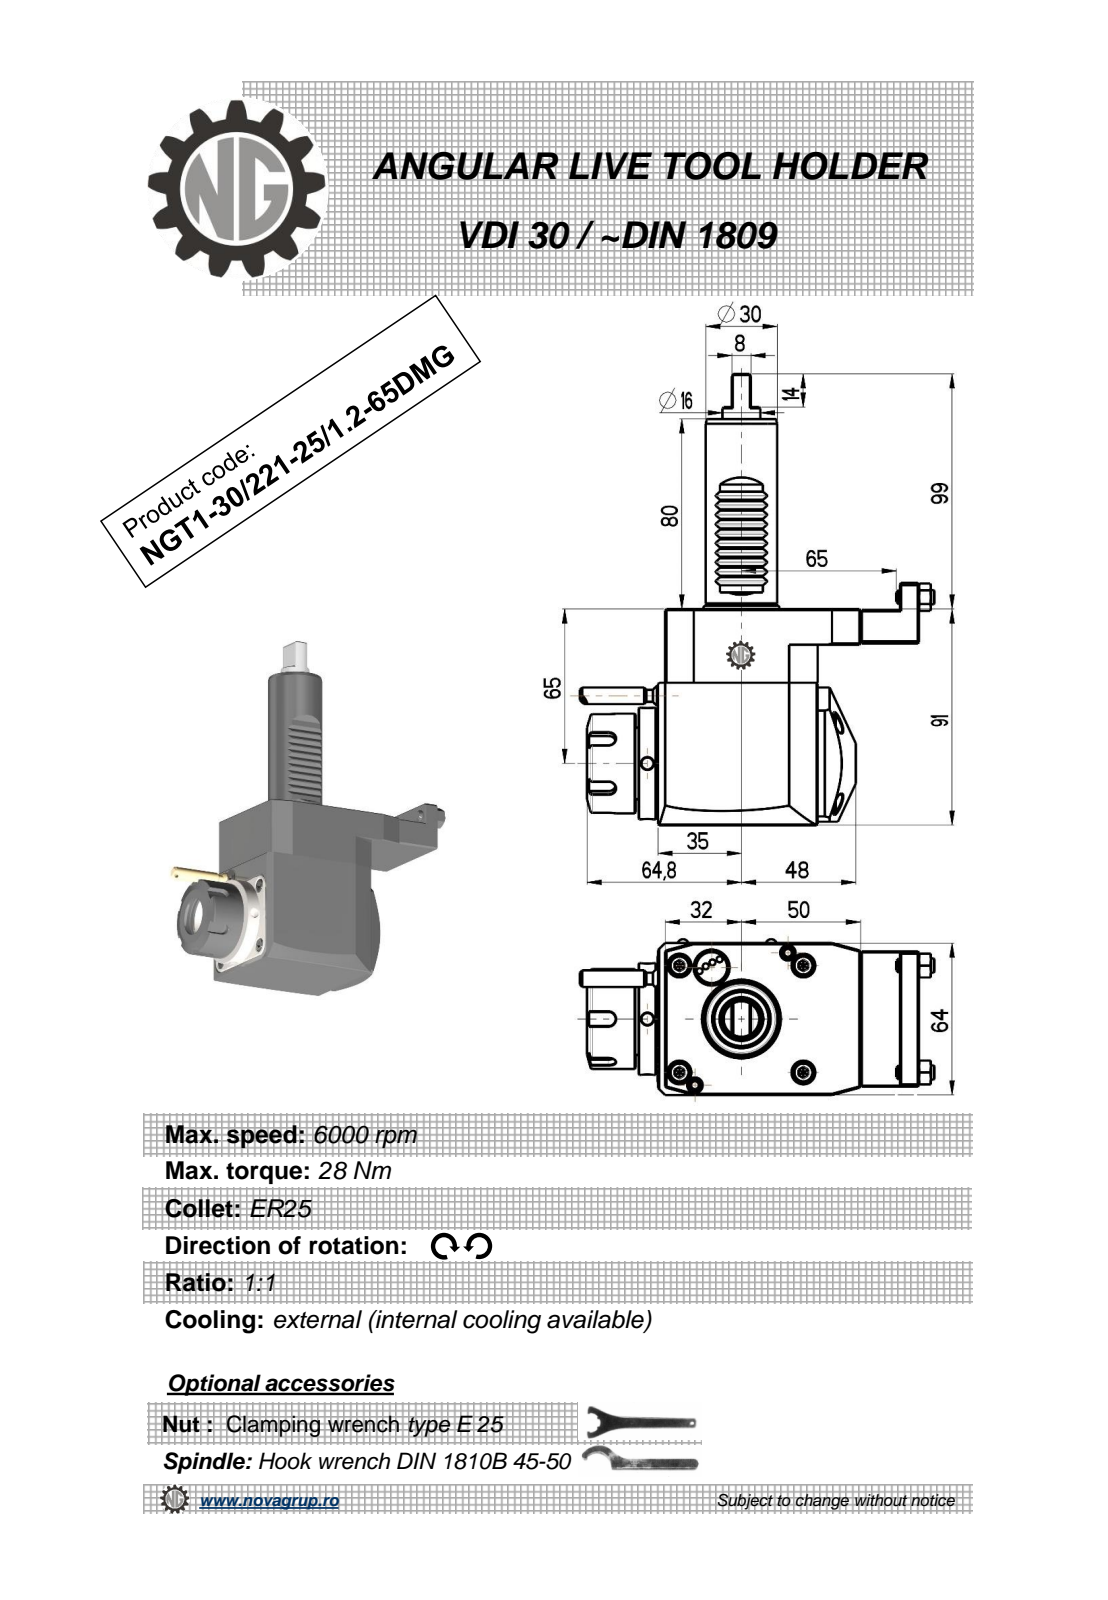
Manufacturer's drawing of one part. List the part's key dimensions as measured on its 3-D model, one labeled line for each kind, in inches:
Part name (STEP PRODUCT): NGT1_30_225_25_1_2_65DMG
STEP written by: PRO/ENGINEER BY PARAMETRIC TECHNOLOGY CORPORATION, 2010280 (CONFIG_CONTROL_DESIGN)
Units: inches
Bodies: 1 solid, 416 faces (182 planar, 74 cylindrical, 160 other)
Overall size (bounding box): 7.48 × 5.859 × 2.52
Volume: 33.24 in³ · Surface area: 89.7 in²
Round holes (diameter × count): ⌀0.197 ×2, ⌀0.098 ×1, ⌀0.118 ×1, ⌀0.799 ×1
Round bosses / shafts (diameter × count): ⌀0.236 ×2, ⌀1.85 ×1, ⌀1.654 ×1, ⌀1.378 ×1, ⌀1.299 ×1, ⌀1.181 ×1, ⌀0.626 ×1, ⌀0.353 ×1
Partial cylindrical surfaces — rounded edges, fillets, slot ends (radius × count): R0.012 ×10, R0.012 ×10, R0.118 ×5, R0.031 ×2, R0.138 ×2, R1.26 ×1
Main face-to-face distances: 2.52, 3.583, 0.02, 0.571, 4.319, 0.315, 3.012, 1.673, 0.126, 2.646
Hole centre spacings: 1.307
